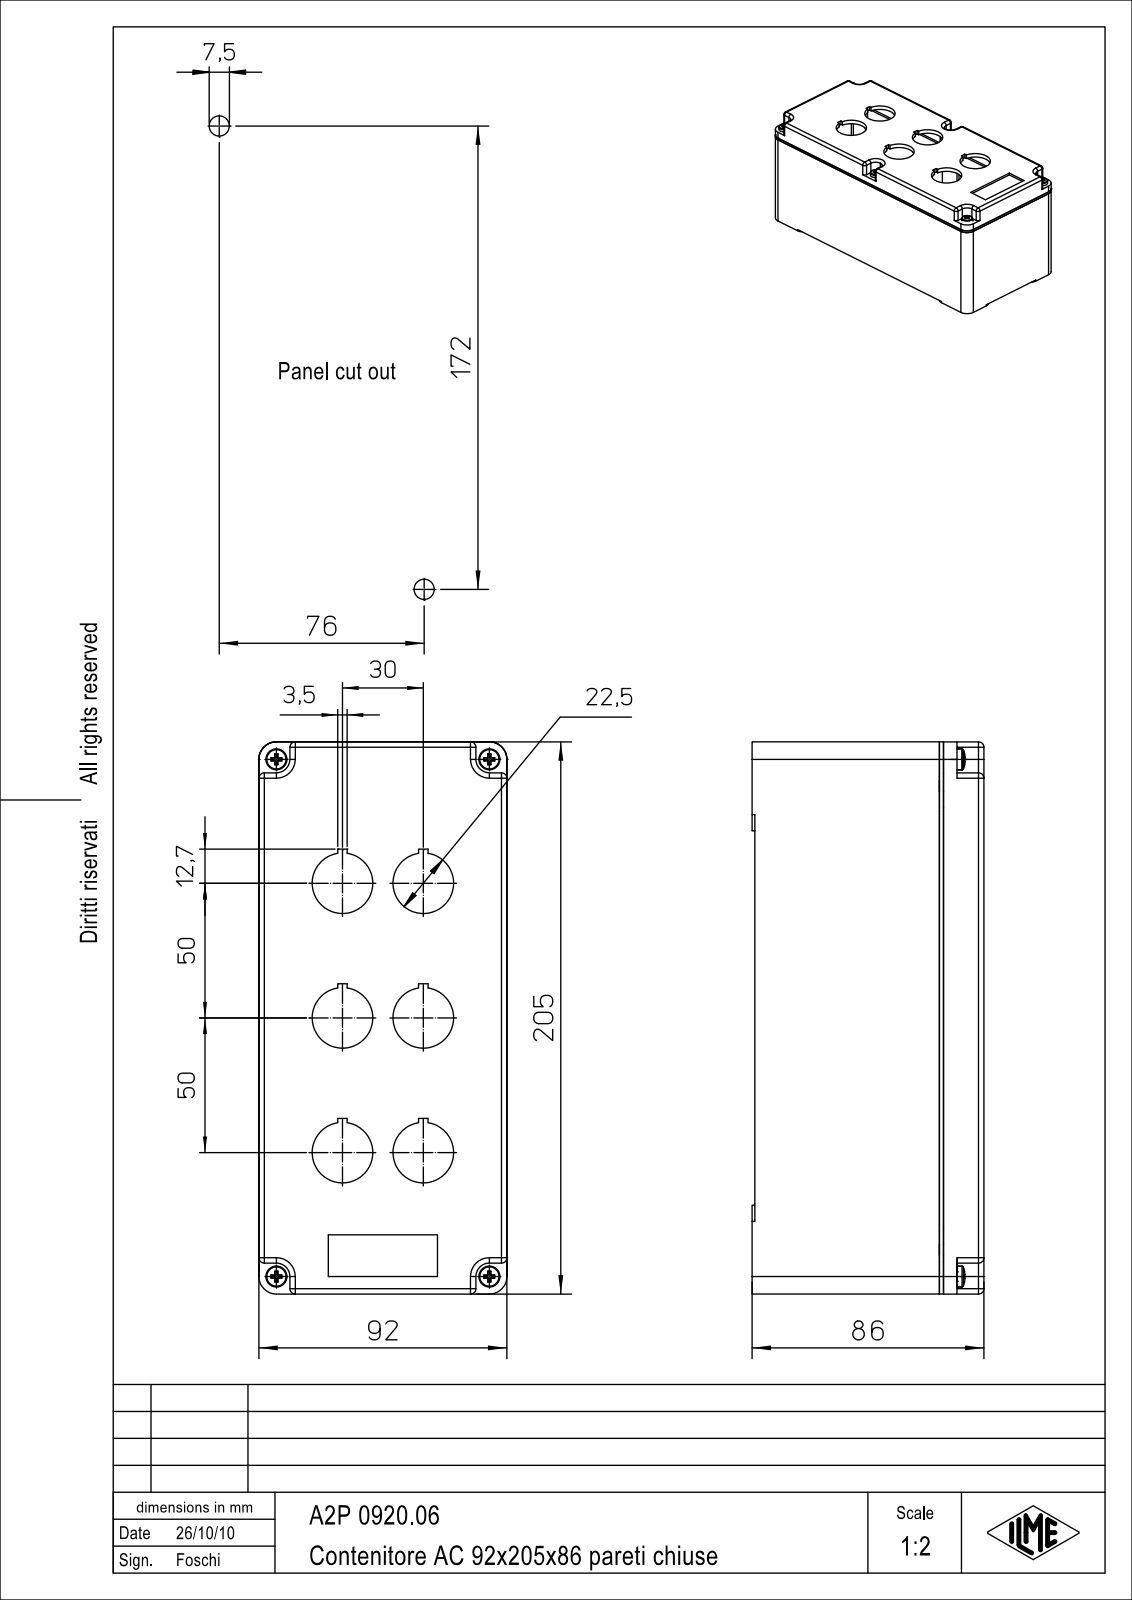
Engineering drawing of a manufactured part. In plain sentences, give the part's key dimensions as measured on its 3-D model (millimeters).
The part is named "COPERCHIO_C_0920.06; CASSETTA_P_0920; GUARNIZIONE_0920; VITE_M4X20 (+2 more)". Its 3-D file was written by "Creo Elements/Direct Modeling 18.1F 24-Jul-2014 (C) Parametric Technology GmbH (AUTOMOTIVE_DESIGN)". It is 11 solids with 1193 faces: 871 planar, 268 cylindrical and 54 other. Overall it measures 205 by 92 by 86 millimeters. Its volume is 357 778 cubic millimeters and its surface area 197 933 square millimeters. Round holes: 8 of diameter 3.3, 8 of diameter 3.8, 6 of diameter 4.5, 6 of diameter 5, 6 of diameter 6, 6 of diameter 22.5, 2 of diameter 5.8, 2 of diameter 7.5, 1 of diameter 10.6, 1 of diameter 10.61. Round bosses or shafts: 9 of diameter 4, 6 of diameter 7.8, 6 of diameter 3.5, 2 of diameter 6.2, 2 of diameter 6, 1 of diameter 7. Partial cylindrical surfaces (rounded edges, fillets, slot ends): 22 of radius 0.33, 22 of radius 2, 12 of radius 6, 8 of radius 5, 8 of radius 6.5, 8 of radius 8, 4 of radius 0.27, 4 of radius 0.27. The main face-to-face distances are 3, 82, 92, 4.38, 4.37, 85, 79, 83.25, 1.5, 87.62. The hole center spacings are 79, 124.33, 96, 71.32, 24.5, 50, 52.12, 54.5.
